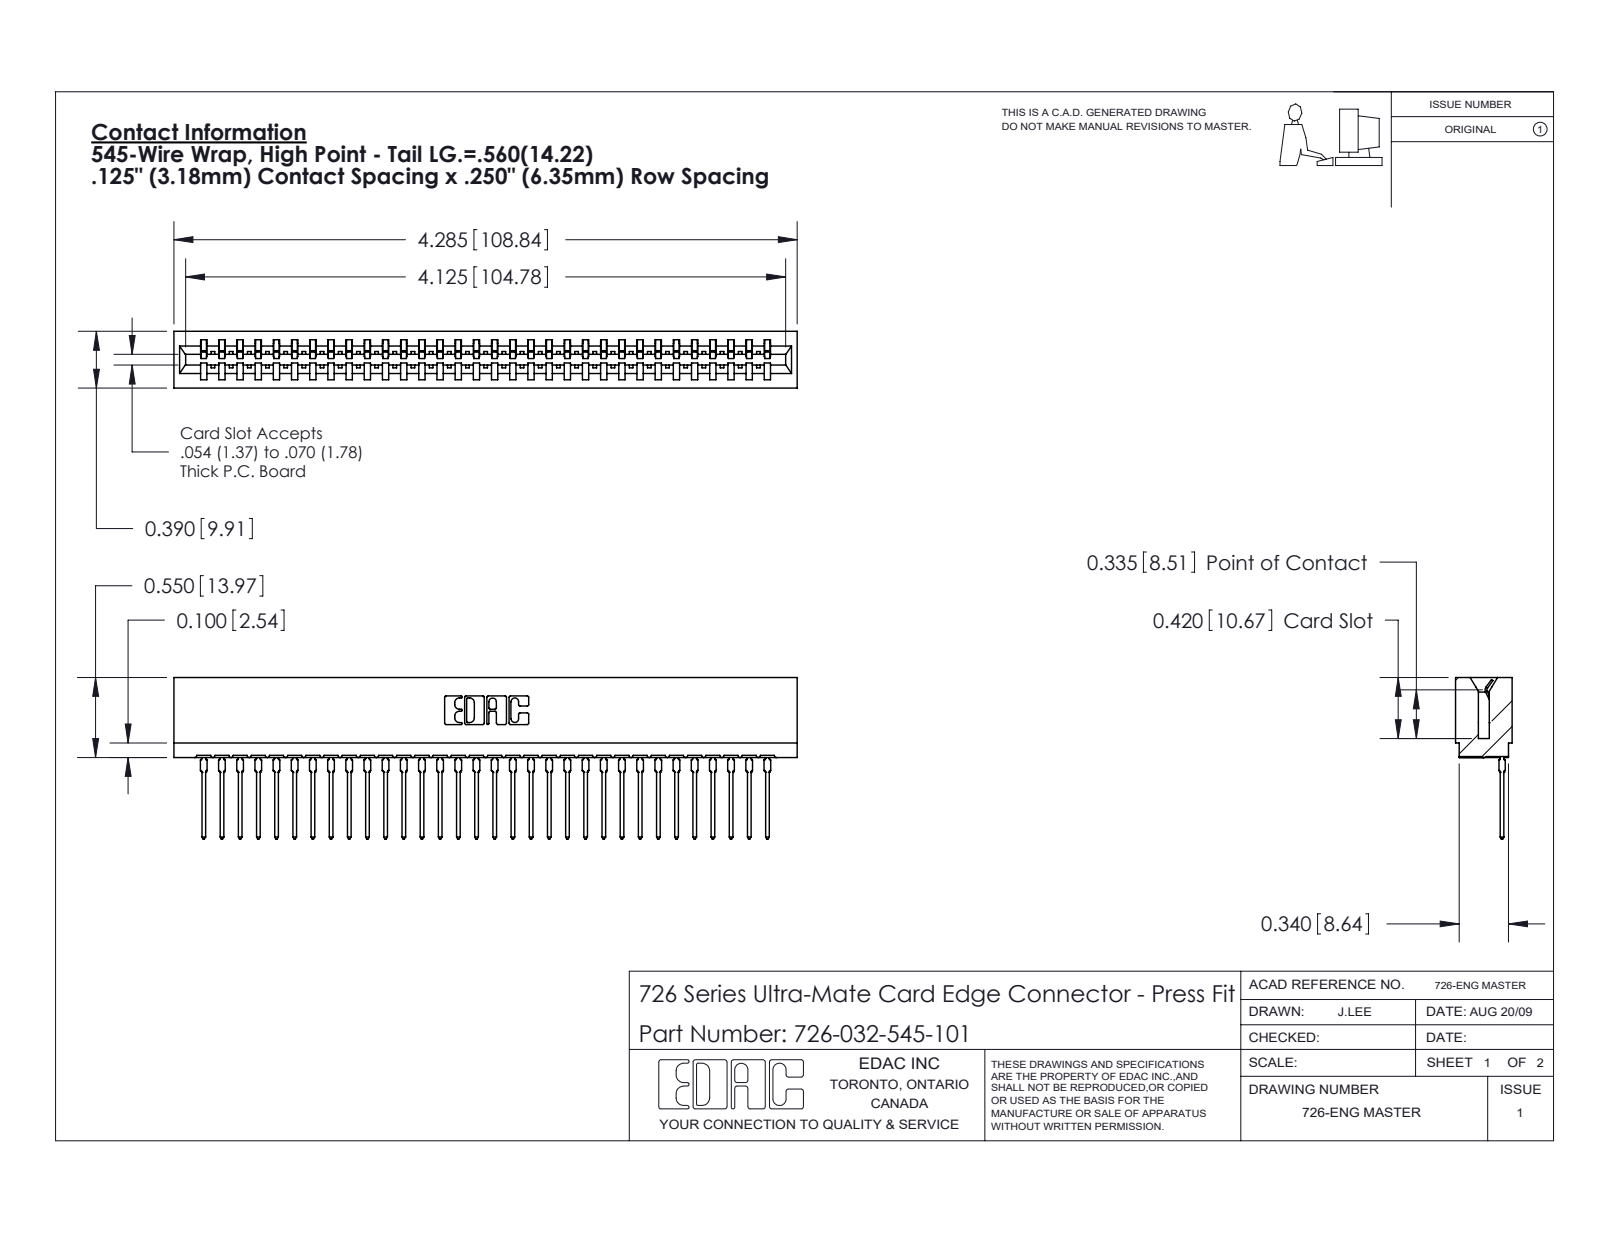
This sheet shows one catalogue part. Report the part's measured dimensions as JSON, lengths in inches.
{"part_name": "746-292-001_545; 726-032-545-101; 726 Part_.515 Slot Depth - 01", "step_written_by": "SolidWorks 2020 (CONFIG_CONTROL_DESIGN)", "units": "inches", "bodies": {"solids": 33, "faces": 3553, "planar": 2071, "cylindrical": 650, "other": 832}, "overall_size": [4.285, 1.109, 0.39], "volume_in3": 0.602, "surface_area_in2": 23.8, "partial_cylinders_radius": [[0.021, 64], [0.015, 33], [0.01, 22], [0.007, 6], [0.031, 6], [0.005, 4], [0.011, 4], [0.026, 3]], "face_to_face_distances": [0.057, 0.333, 0.39, 0.25, 0.025, 0.307, 0.083, 0.275, 0.365, 0.032]}
